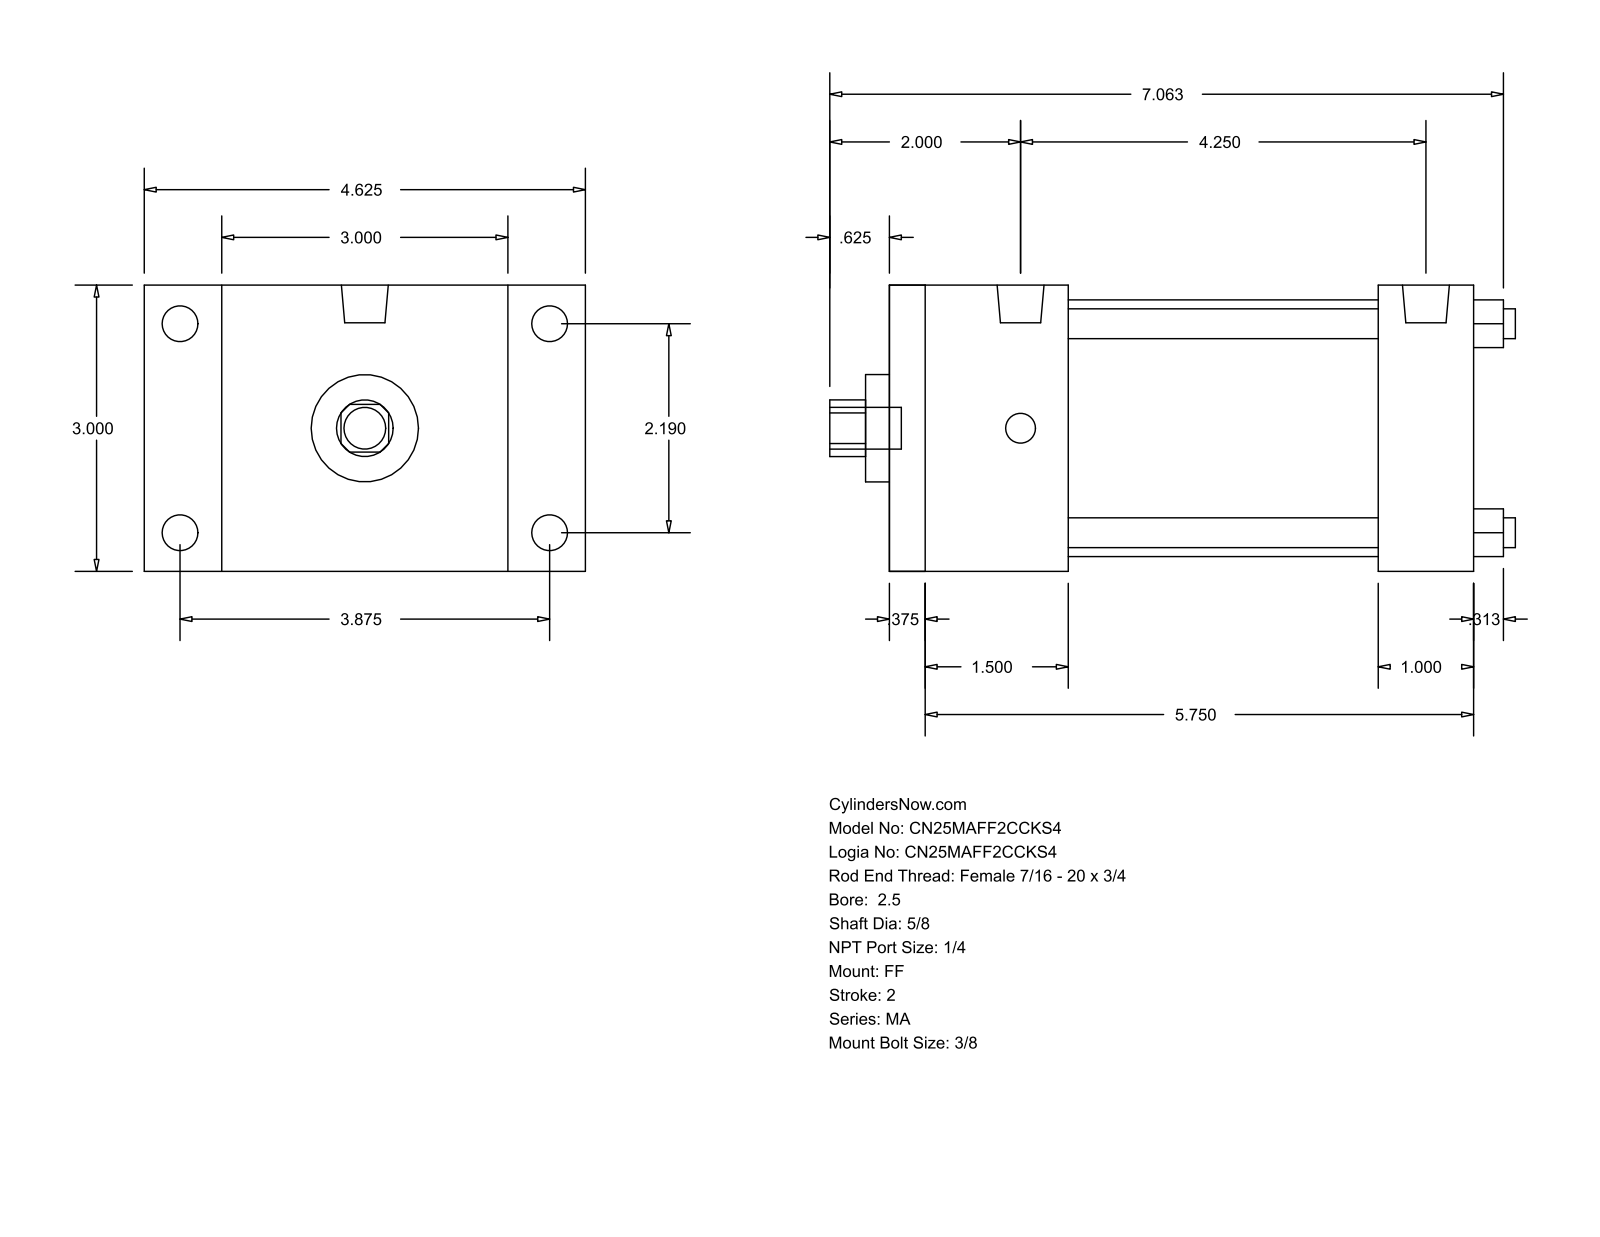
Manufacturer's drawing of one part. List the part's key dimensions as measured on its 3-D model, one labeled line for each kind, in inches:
Part name (STEP PRODUCT): MA_FF__0250_0.625
STEP written by: GSSL Pune (CONFIG_CONTROL_DESIGN)
Units: inches
Bodies: 0 solids, 92 faces (64 planar, 28 cylindrical, 0 other)
Overall size (bounding box): 7.187 × 4.625 × 3
Round holes (diameter × count): ⌀0.313 ×4, ⌀0.625 ×1, ⌀1.125 ×1, ⌀2.69 ×1
Round bosses / shafts (diameter × count): ⌀0.375 ×4, ⌀0.313 ×4, ⌀0.492 ×2, ⌀0.437 ×1
Partial cylindrical surfaces — rounded edges, fillets, slot ends (radius × count): R0.297 ×1
Main face-to-face distances: 3, 6.125, 0.375, 5.75, 1, 1.875, 5.125, 1.5, 4.75, 3.25
Hole centre spacings: 1.548, 2.19, 3.097
